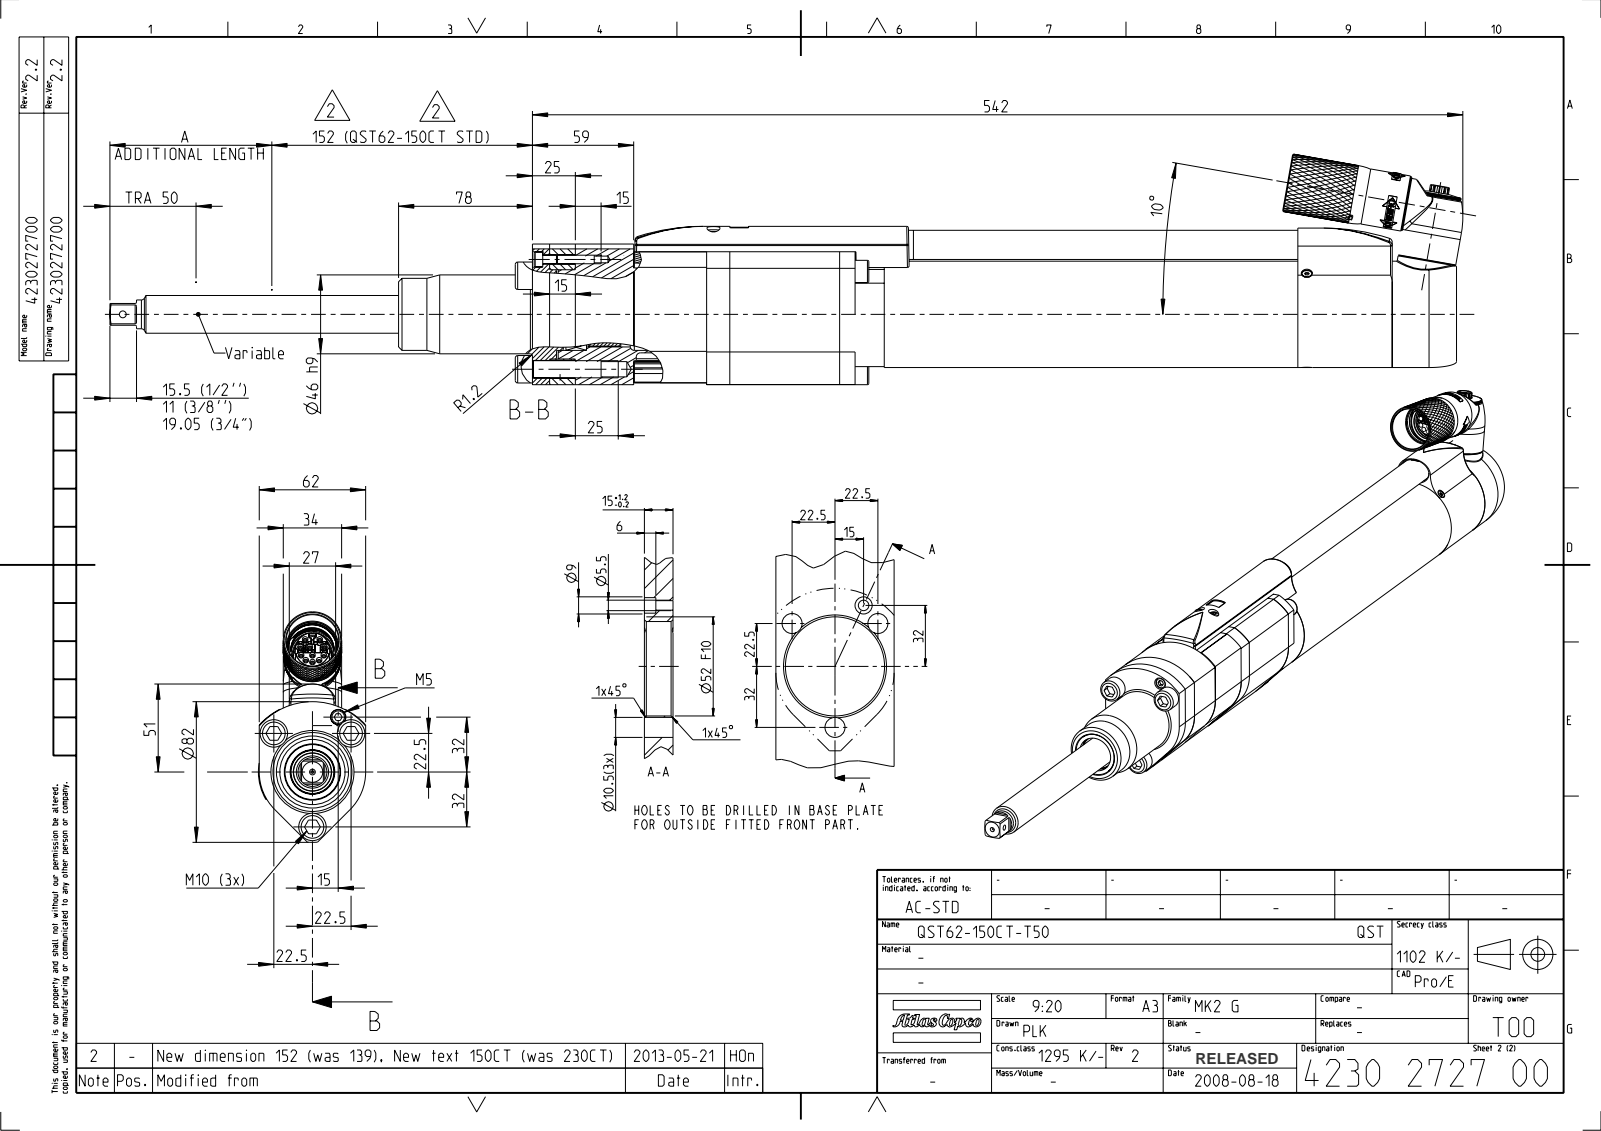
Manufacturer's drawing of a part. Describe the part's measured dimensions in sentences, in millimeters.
The part is named "QST62_REARCOVER_02; QST_CONNECTOR_02; QST62_150_CT_BODY_50; QST62_SPACER_01 (+3 more)". Its 3-D file was written by "PRO/ENGINEER BY PARAMETRIC TECHNOLOGY CORPORATION, 2012420 (CONFIG_CONTROL_DESIGN)". It is 7 solids with 3301 faces: 1305 planar, 1046 cylindrical and 950 other. Overall it measures 694.18 by 134.4 by 62 millimeters. Its volume is 1 252 000 cubic millimeters and its surface area 420 234 square millimeters. Round holes: 9 of diameter 3.3, 9 of diameter 4.5, 4 of diameter 3.92, 4 of diameter 5.5, 4 of diameter 7.5, 4 of diameter 9, 3 of diameter 1.9, 3 of diameter 3.5, 3 of diameter 6.92, 3 of diameter 8.5, 3 of diameter 8.92, 3 of diameter 10.3. Round bosses or shafts: 5 of diameter 5, 5 of diameter 3, 5 of diameter 2.5, 4 of diameter 34, 4 of diameter 8.5, 4 of diameter 8, 3 of diameter 16, 3 of diameter 13. Partial cylindrical surfaces (rounded edges, fillets, slot ends): 45 of radius 0.5, 11 of radius 1, 8 of radius 0.2, 5 of radius 2, 4 of radius 0.68, 4 of radius 1.5, 4 of radius 5.25, 4 of radius 23. The main face-to-face distances are 62, 3.5, 15, 25, 250.5, 513.5, 528.5, 34, 476, 510. The hole center spacings are 22.5, 20.24, 14.79, 16.7, 23.1, 23.11, 28.92, 39.2.
